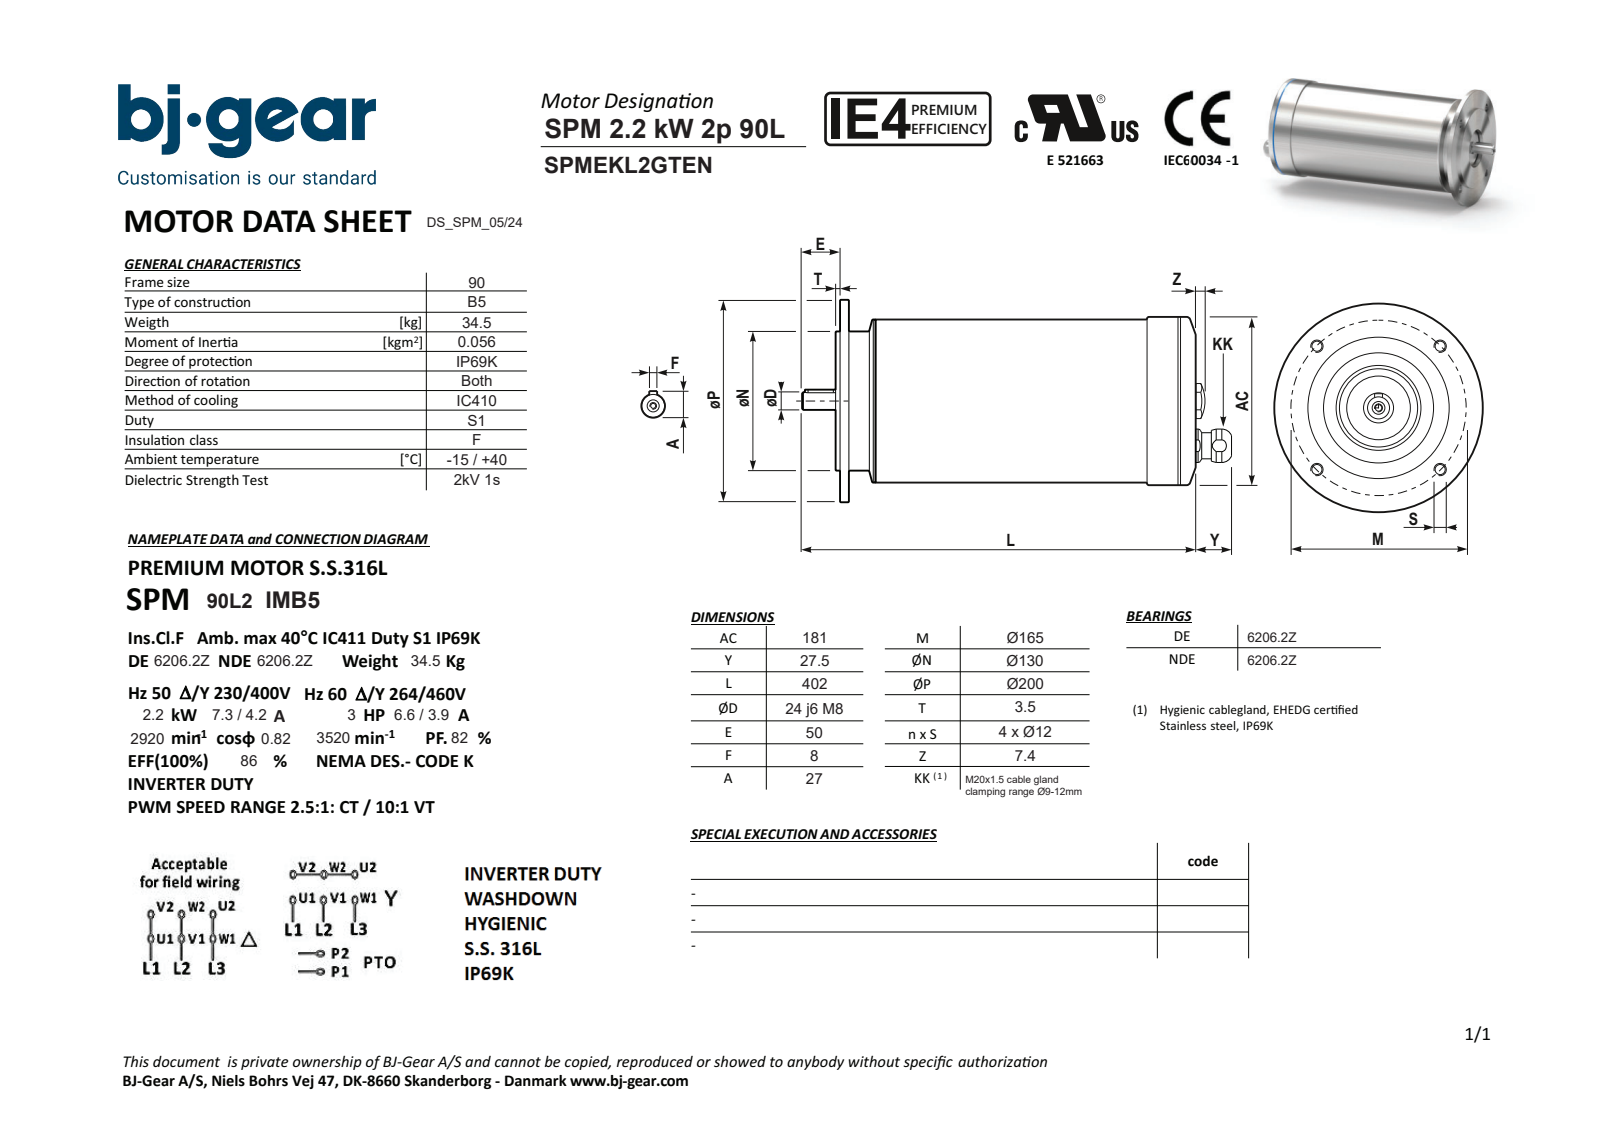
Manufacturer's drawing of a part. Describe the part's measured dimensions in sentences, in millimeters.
The part is named "SPMEKL2GTENN4KSA1-N---NNN". Its 3-D file was written by "Solid Edge (AUTOMOTIVE_DESIGN)". It is 1 solid with 86 faces: 31 planar, 30 cylindrical and 25 other. Overall it measures 429.5 by 200 by 200 millimeters. Its volume is 8 632 000 cubic millimeters and its surface area 282 681 square millimeters. Round holes: 4 of diameter 12, 1 of diameter 4.92, 1 of diameter 7, 1 of diameter 8.4, 1 of diameter 13.4, 1 of diameter 85. Round bosses or shafts: 1 of diameter 200, 1 of diameter 181, 1 of diameter 180.98, 1 of diameter 178, 1 of diameter 177.98, 1 of diameter 142, 1 of diameter 130, 1 of diameter 30. Partial cylindrical surfaces (rounded edges, fillets, slot ends): 2 of radius 4, 1 of radius 12.8. The main face-to-face distances are 352, 8, 344, 355.5, 11.5, 3.5, 6, 2, 346, 9.5. The hole center spacings are 82.51, 116.68, 58.44, 127.47, 165.01, 55.
